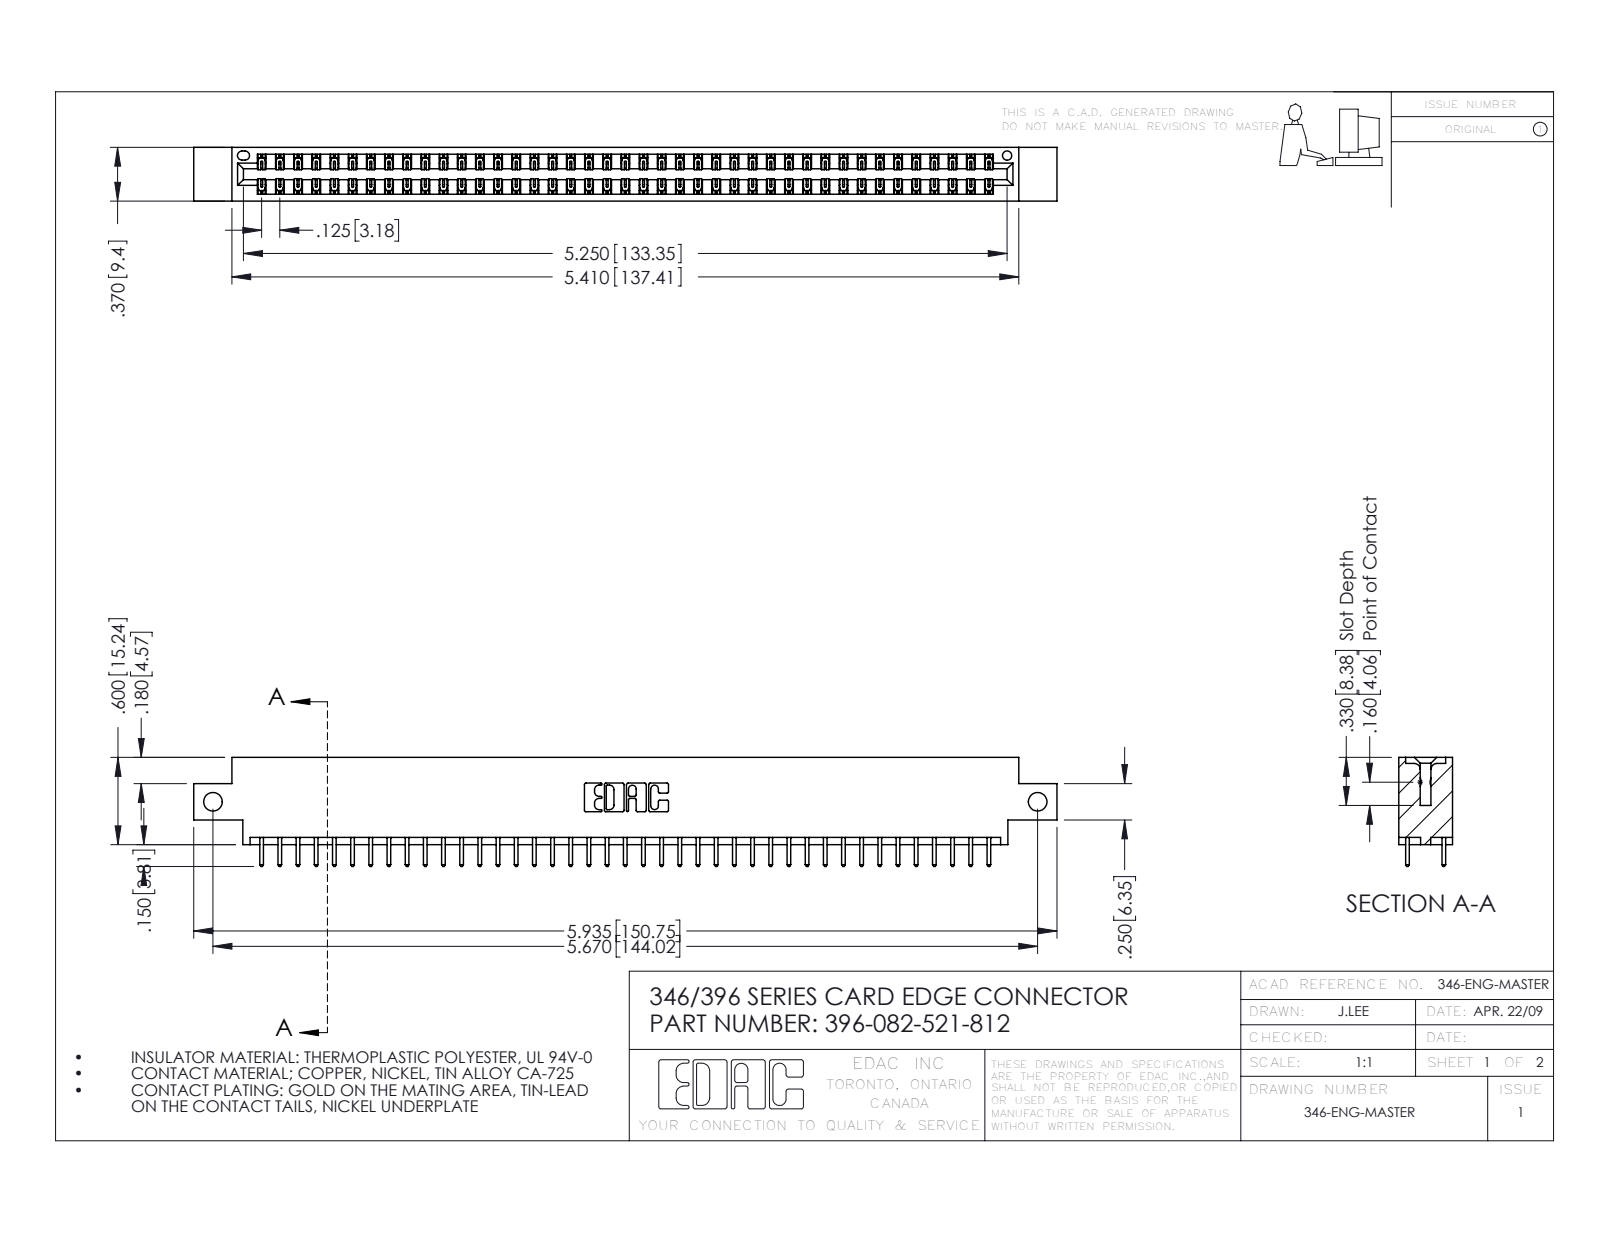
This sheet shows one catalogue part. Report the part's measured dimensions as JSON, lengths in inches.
{"part_name": "346 Part_0.170 Offset - Side Mount; 396-082-521-812; 345-292-001_345-293-121", "step_written_by": "SolidWorks 2016 (CONFIG_CONTROL_DESIGN)", "units": "inches", "bodies": {"solids": 83, "faces": 4390, "planar": 2950, "cylindrical": 1440, "other": 0}, "overall_size": [5.935, 0.75, 0.37], "volume_in3": 0.88, "surface_area_in2": 30.41, "round_holes": [[0.128, 2], [0.064, 1]], "partial_cylinders_radius": [[0.006, 123], [0.01, 82], [0.01, 22], [0.007, 6], [0.031, 6], [0.026, 3], [0.014, 2], [0.022, 2]], "face_to_face_distances": [0.048, 0.322, 0.37, 0.25, 0.072, 0.298, 0.025, 0.275, 0.148, 0.222], "hole_center_spacings": [5.67]}
